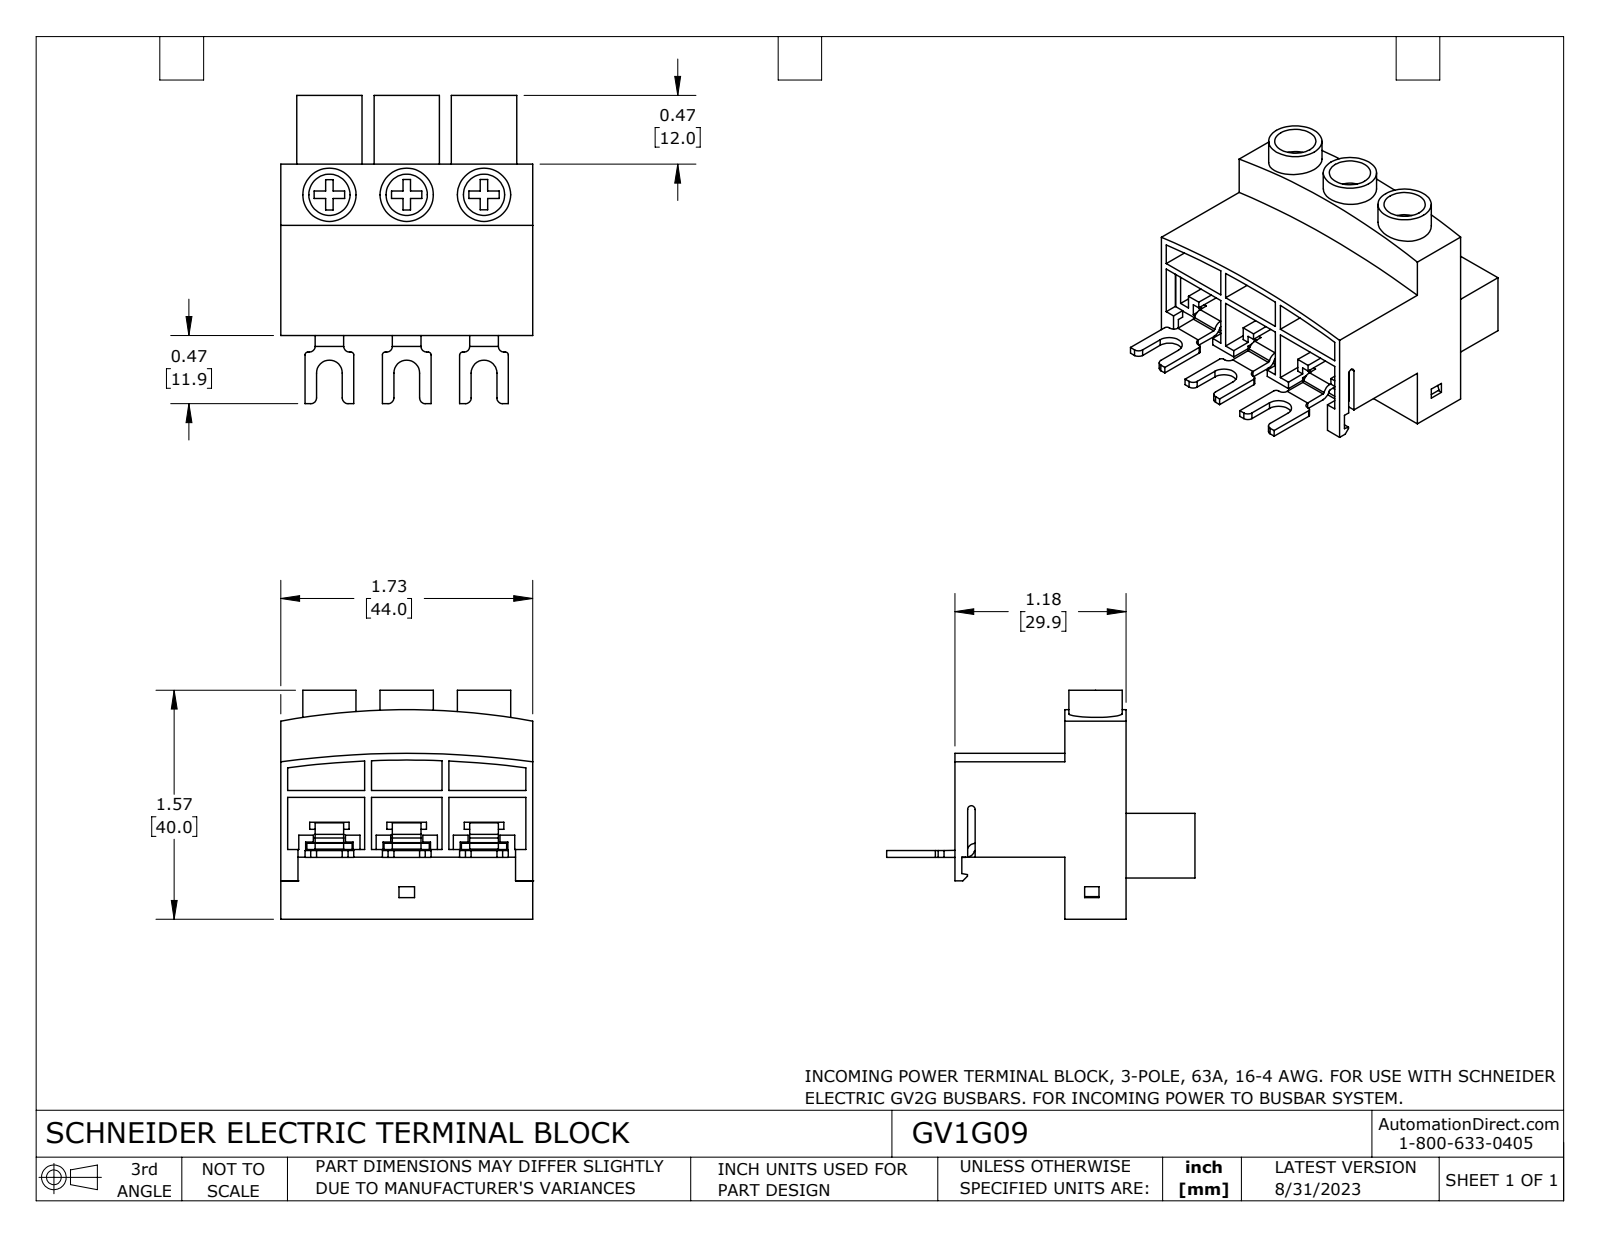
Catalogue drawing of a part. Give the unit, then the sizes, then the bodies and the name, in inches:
Units: inches
Overall size (bounding box): 2.119 × 1.732 × 1.575
Round holes (diameter × count): ⌀0.283 ×3
Round bosses / shafts (diameter × count): ⌀0.366 ×3
Partial cylindrical surfaces — rounded edges, fillets, slot ends (radius × count): R0.039 ×8, R0.012 ×2, R0.031 ×2, R0.059 ×2, R0.079 ×2, R0.026 ×1, R4.803 ×1, R6.331 ×1
Main face-to-face distances: 0.047, 0.531, 0.421, 1.108, 0.577, 0.412, 0.459, 0.555, 0.157, 0.514
Hole centre spacings: 0.531, 1.063
Volume: 1.287 in³ · Surface area: 30.12 in²
Bodies: 1 solid, 464 faces (377 planar, 57 cylindrical, 30 other)
Part name (STEP PRODUCT): GV1G09
STEP written by: SolidWorks 2021 (CONFIG_CONTROL_DESIGN)
